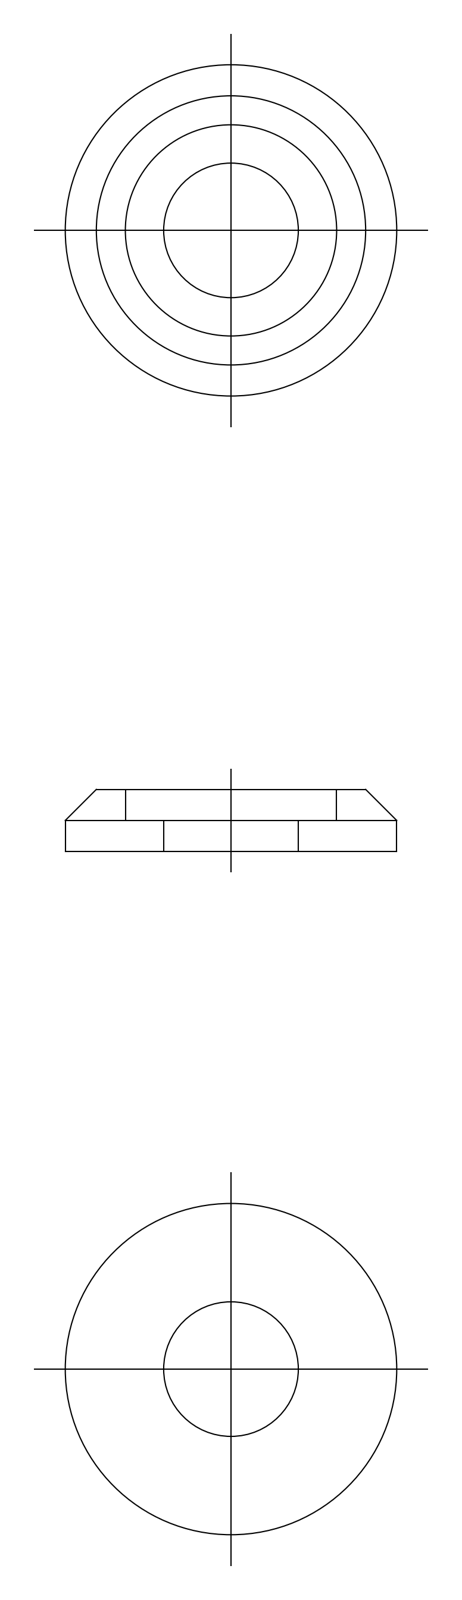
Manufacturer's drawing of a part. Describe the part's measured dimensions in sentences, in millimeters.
The part is named "facing ring". Its 3-D file was written by "CADfix (AUTOMOTIVE_DESIGN)". It is 1 solid with 11 faces: 0 planar, 0 cylindrical and 11 other. Overall it measures 16 by 16 by 3 millimeters. Its volume is 379 cubic millimeters and its surface area 518 square millimeters.
